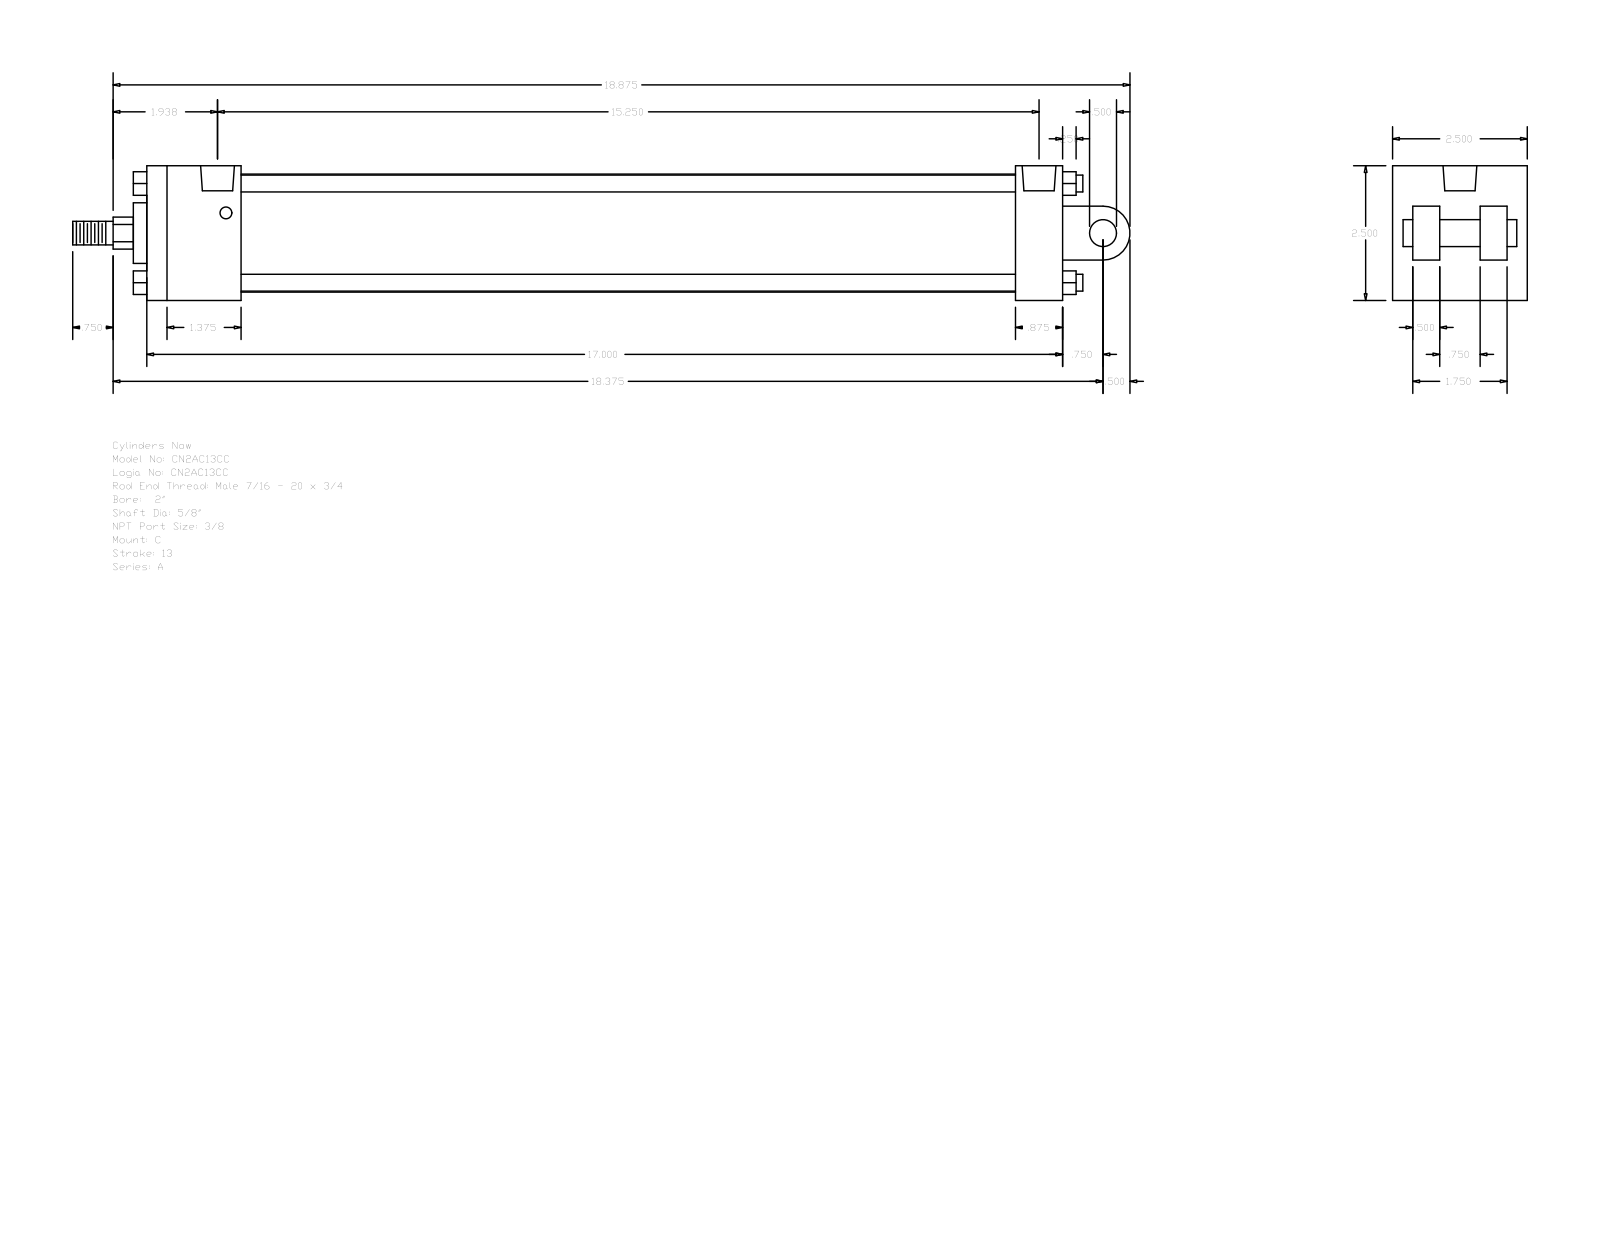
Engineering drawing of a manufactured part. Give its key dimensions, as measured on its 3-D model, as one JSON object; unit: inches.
{"part_name": "A_C__0200_0.625", "step_written_by": "GSSL Pune (CONFIG_CONTROL_DESIGN)", "units": "inches", "bodies": {"solids": 0, "faces": 135, "planar": 102, "cylindrical": 33, "other": 0}, "overall_size": [19.625, 2.5, 2.5], "round_holes": [[0.219, 4], [0.627, 2]], "round_bosses_or_shafts": [[0.313, 4], [2.19, 1], [1.125, 1], [0.625, 1], [0.5, 1], [0.437, 1]], "partial_cylinders_radius": [[0.297, 1], [0.5, 1]], "face_to_face_distances": [2.5, 17, 1.75, 0.375, 15.25, 16.125, 14.375, 0.875, 0.5, 2.125], "hole_center_spacings": [14.937, 0.156, 0.157, 15.093, 15.094, 15.25]}
